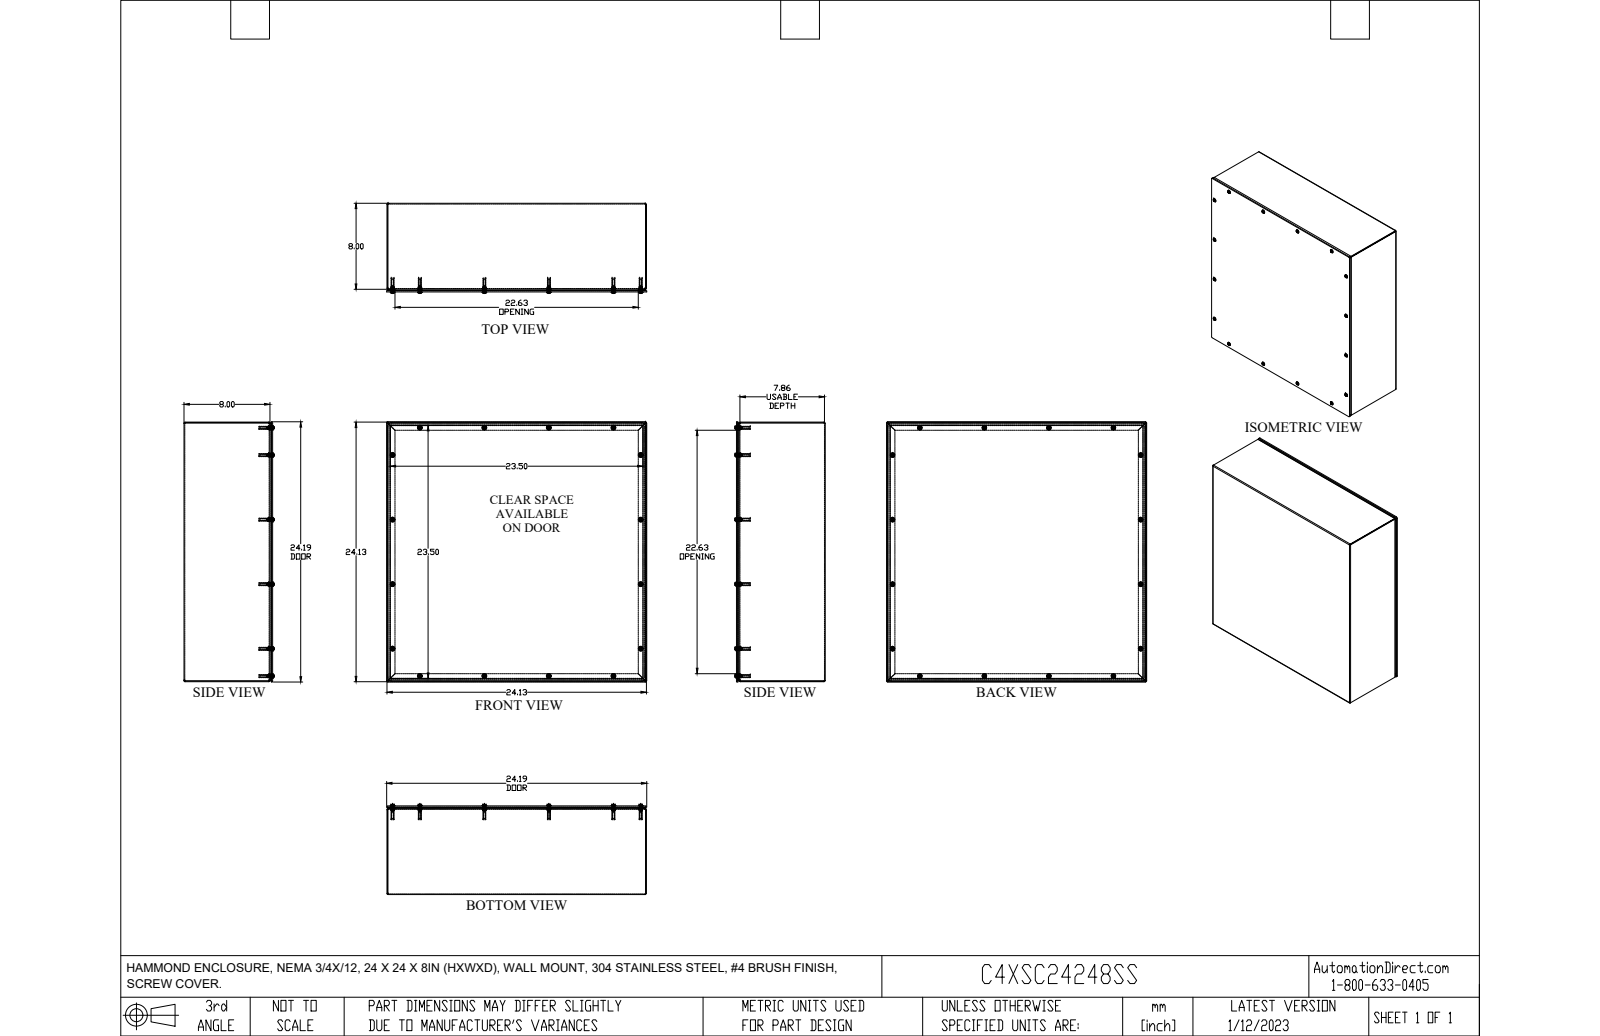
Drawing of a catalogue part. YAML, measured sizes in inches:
part_name: "C3SC24248GY"
step_written_by: "SolidWorks 2021 (AUTOMOTIVE_DESIGN)"
units: inches
bodies: {solids: 51, faces: 1476, planar: 920, cylindrical: 272, other: 284}
overall_size: [24.188, 24.188, 8.4]
volume: 174.5
surface_area: 4147
round_holes:
  - {diameter: 0.159, count: 16}
  - {diameter: 0.16, count: 16}
  - {diameter: 0.25, count: 16}
round_bosses_or_shafts:
  - {diameter: 0.44, count: 16}
  - {diameter: 0.39, count: 16}
  - {diameter: 0.24, count: 16}
  - {diameter: 0.19, count: 16}
  - {diameter: 0.148, count: 16}
  - {diameter: 0.275, count: 12}
  - {diameter: 0.275, count: 4}
partial_cylinders:
  - {radius: 0.16, count: 16}
  - {radius: 0.04, count: 8}
  - {radius: 0.11, count: 8}
  - {radius: 0.125, count: 8}
  - {radius: 0.126, count: 4}
  - {radius: 0.374, count: 4}
face_to_face_distances: [0.07, 0.125, 8.25, 8.125, 8.18, 8.055, 24.13, 24.06, 24.06, 0.07]
hole_center_spacings: [6, 23.842, 8.906, 12, 14.757, 16.859, 20.694, 22.241]
